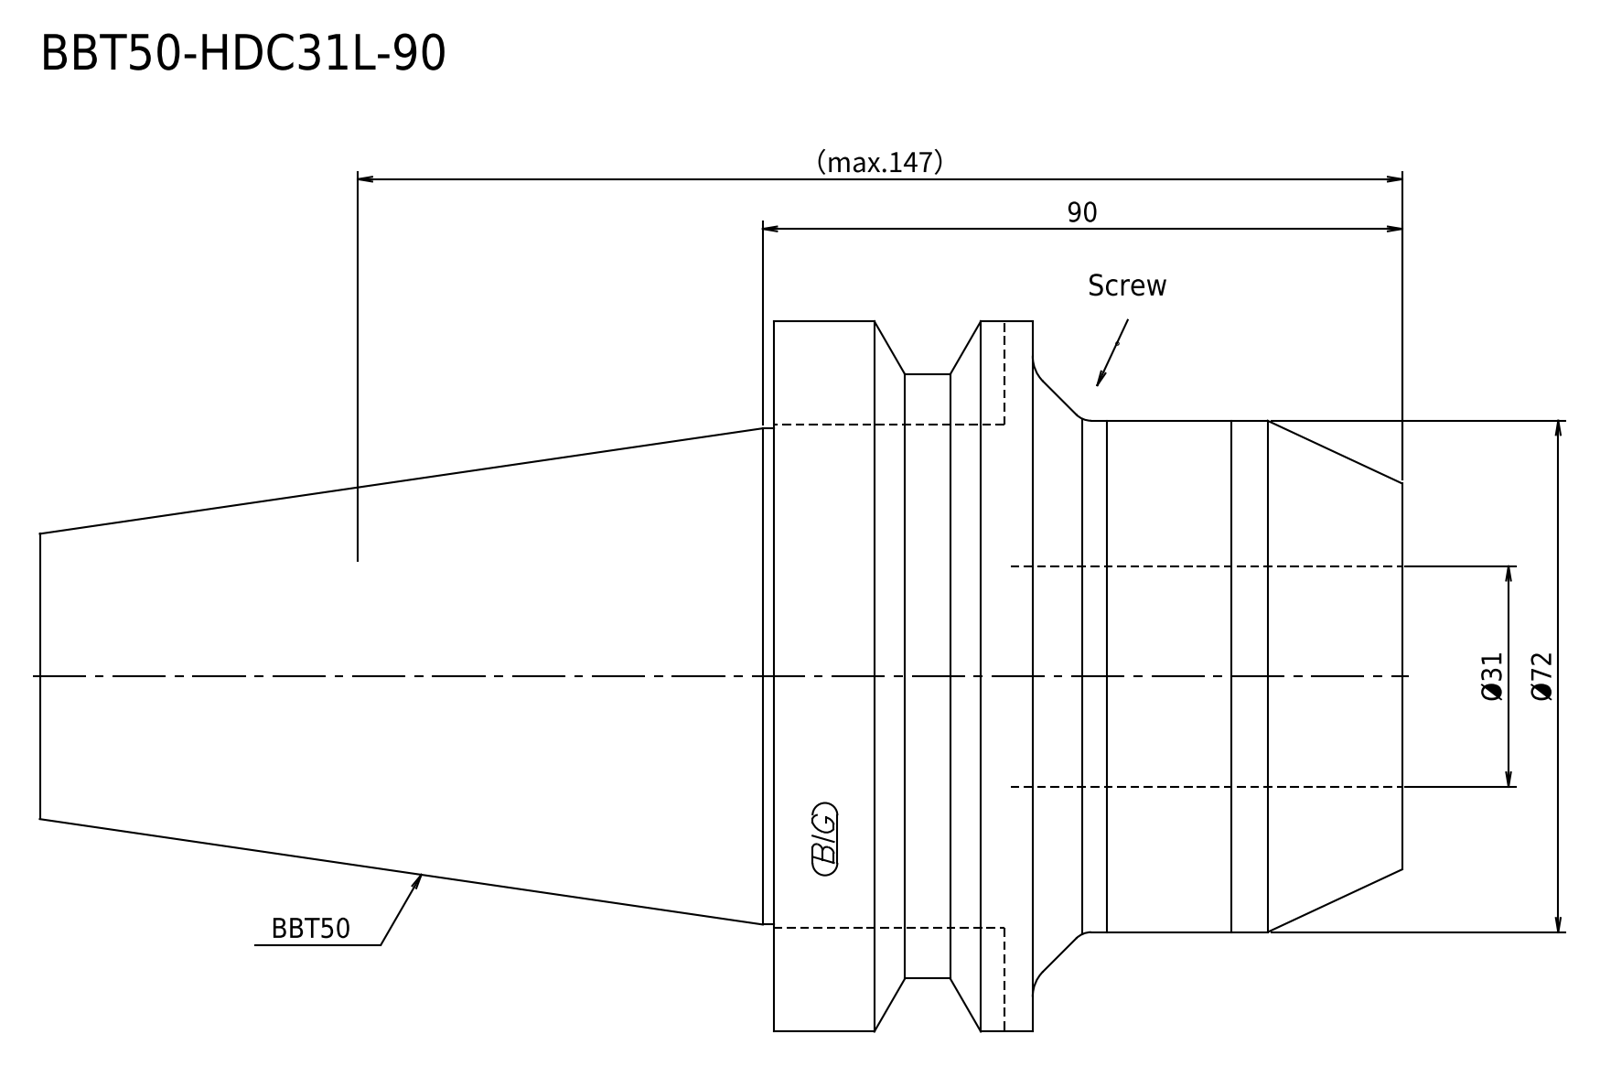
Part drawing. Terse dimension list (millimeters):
written by: Kubotek KeyCreator V8.5.1 (14335) (CONFIG_CONTROL_DESIGN)
unit: mm
bodies: 1 solid, 18 faces (5 planar, 5 cylindrical, 8 other)
size: 191.8 × 100 × 100
volume: 716 823 mm³; area: 53 580 mm²
bosses: 1× ⌀100, 1× ⌀85, 1× ⌀72, 1× ⌀69.85
face distances: 36.5, 52, 88.5, 191.8, 139.8, 103.3, 0.7, 51.3, 87.8, 191.1
